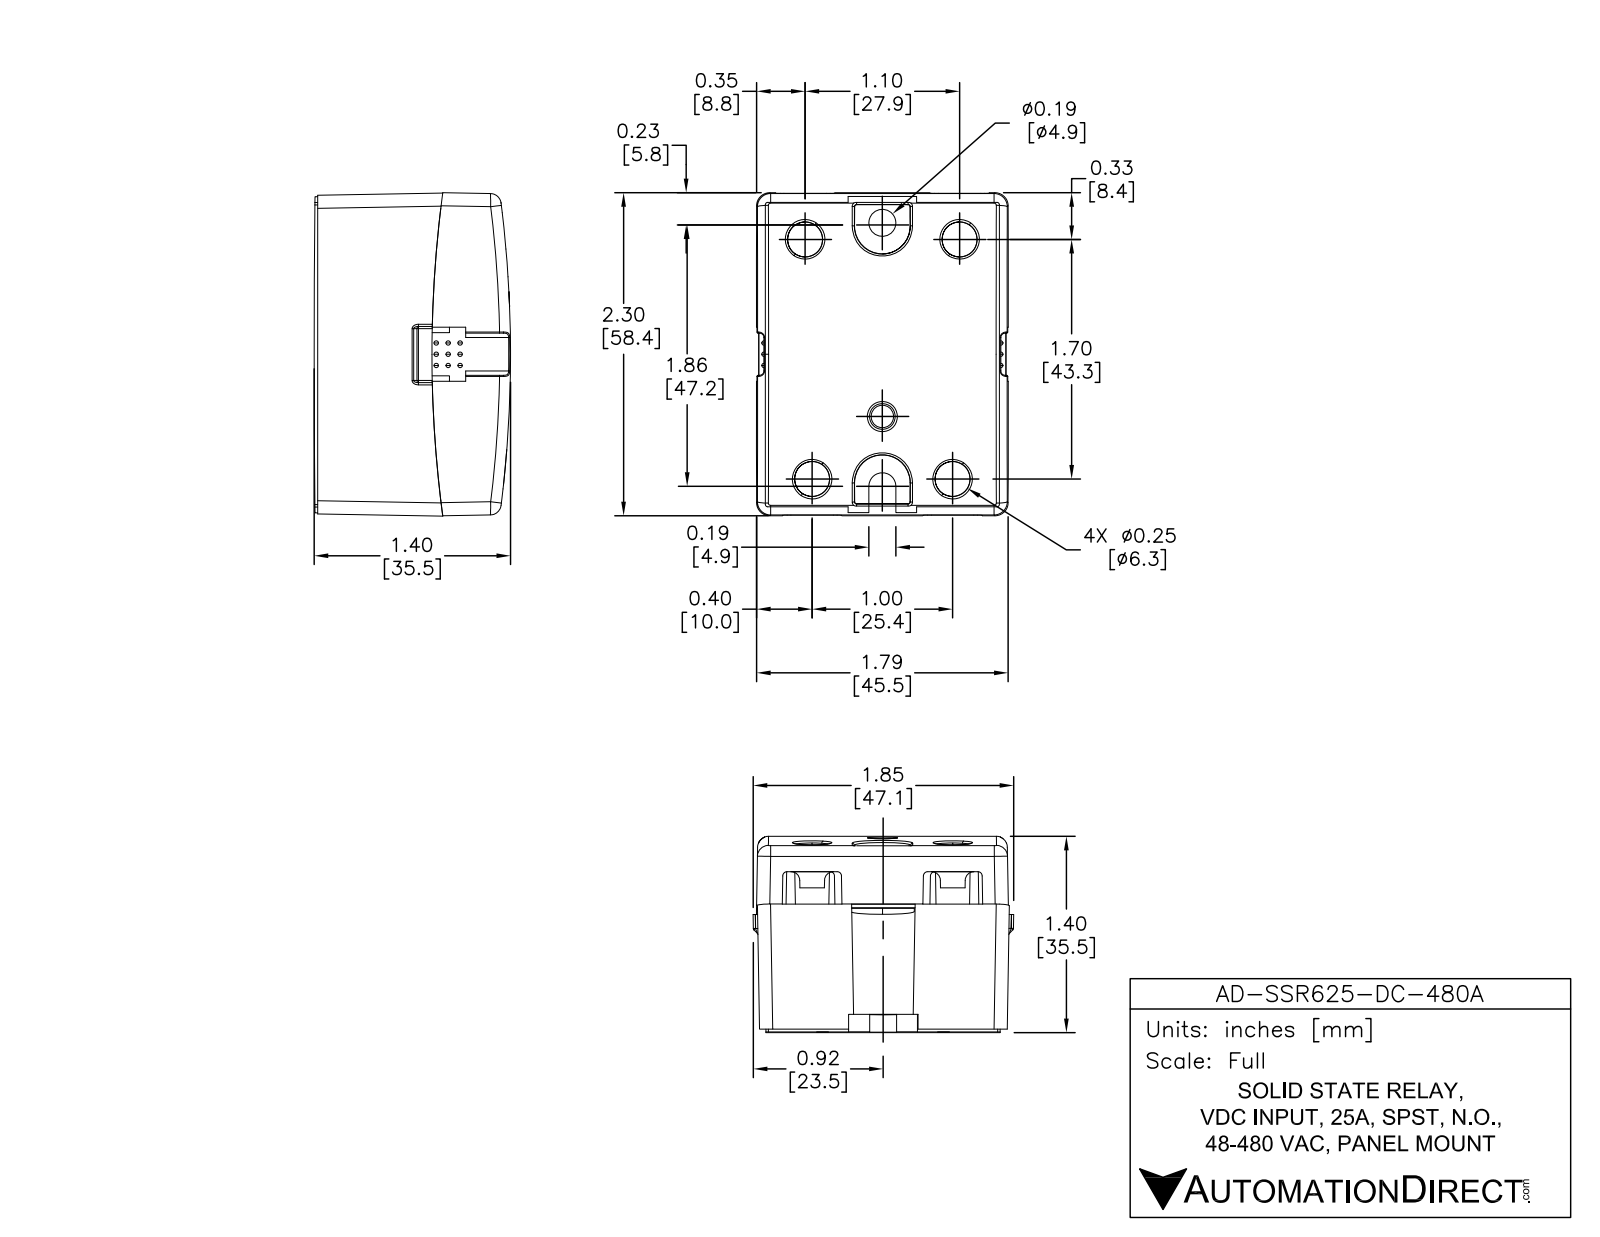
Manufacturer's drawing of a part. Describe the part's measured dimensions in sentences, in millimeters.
The part is named "AD-SSR625-DC-480A". Its 3-D file was written by "SolidWorks 2013 (AUTOMOTIVE_DESIGN)". It is 3 solids with 251 faces: 145 planar, 95 cylindrical and 11 other. Overall it measures 58.4 by 45.5 by 35.6 millimeters. Its volume is 84 230 cubic millimeters and its surface area 17 040 square millimeters. Round holes: 4 of diameter 6.4, 1 of diameter 4.8. Round bosses or shafts: 2 of diameter 10.2, 2 of diameter 8.9, 2 of diameter 7.6, 2 of diameter 6.4, 2 of diameter 5.1, 2 of diameter 5.1. Partial cylindrical surfaces (rounded edges, fillets, slot ends): 6 of radius 0.8, 4 of radius 0.3, 4 of radius 1, 4 of radius 12.7, 2 of radius 4.9, 1 of radius 2.4, 1 of radius 12.7, 1 of radius 12.7. The main face-to-face distances are 45.5, 58.4, 29.6, 6.4, 23.3, 17, 26.9, 12.7, 45.7, 2. The hole center spacings are 14.1, 14.4, 25.4, 27.9, 43.2, 43.2, 47.7, 47.7.
